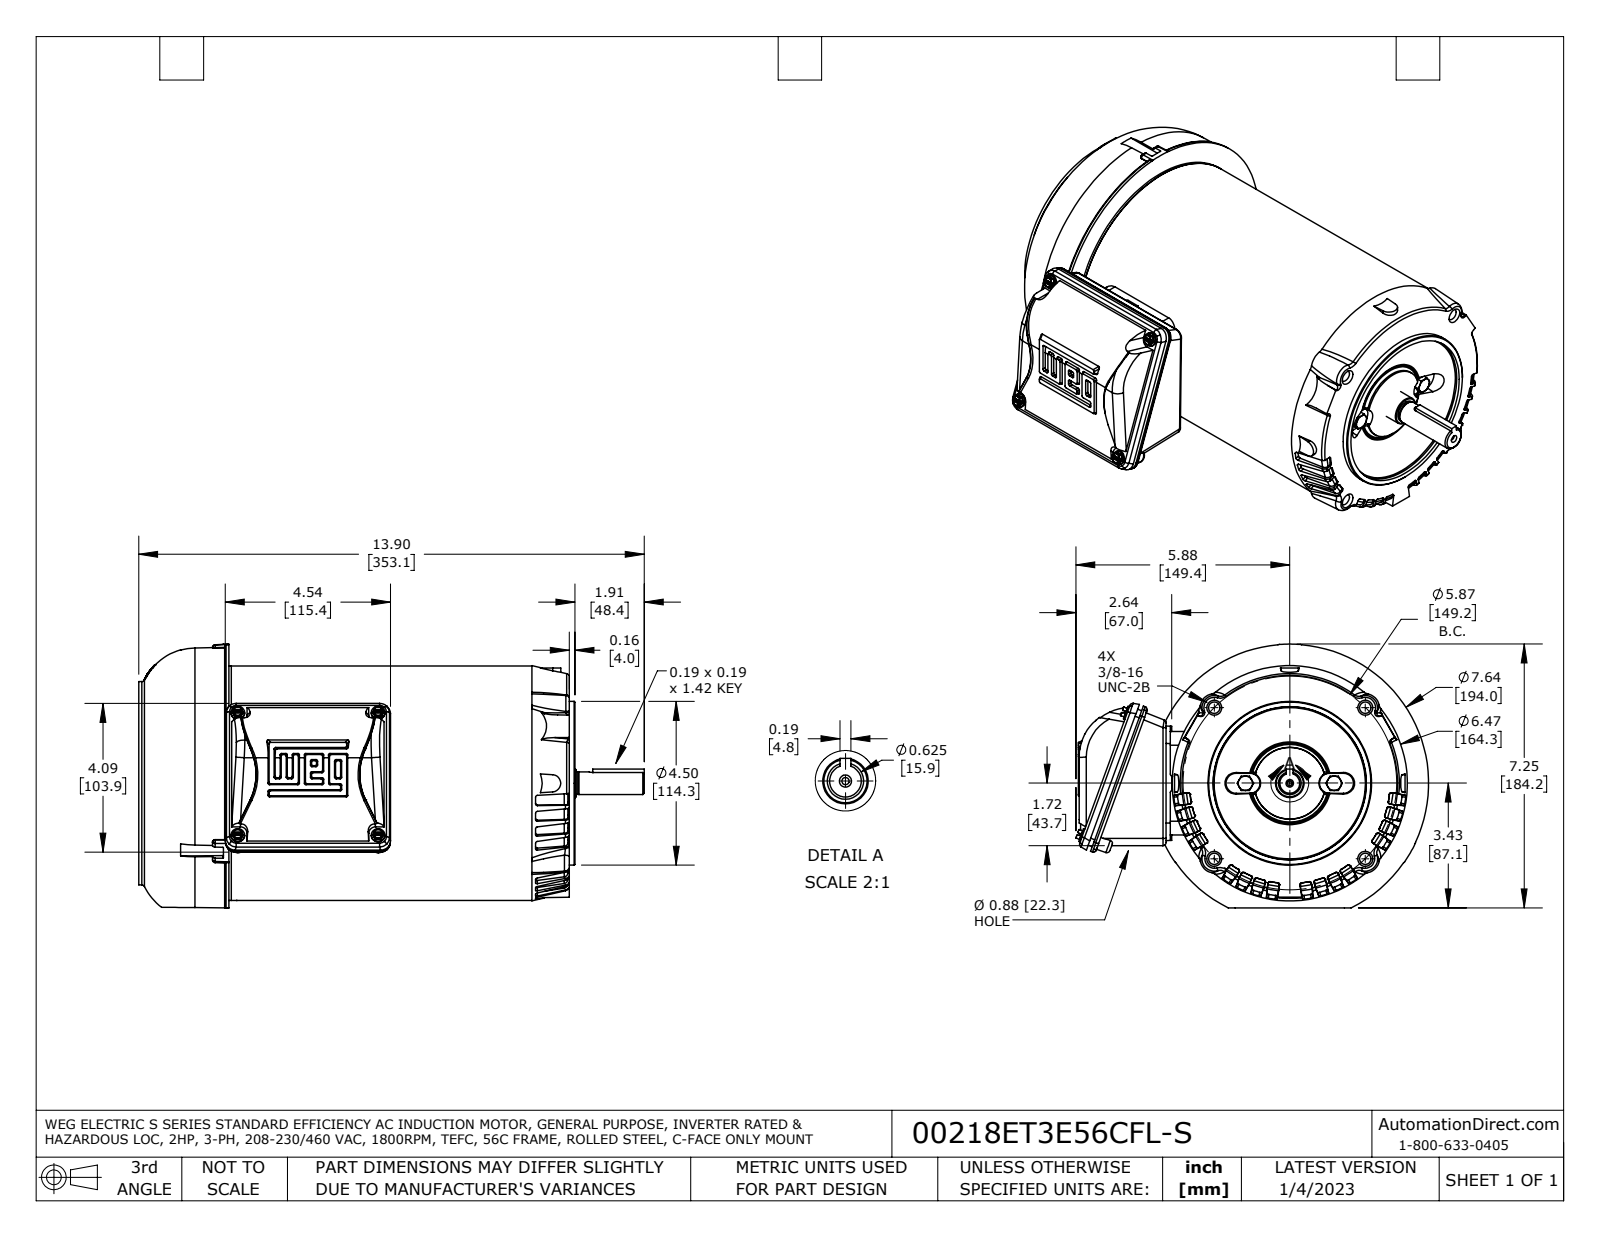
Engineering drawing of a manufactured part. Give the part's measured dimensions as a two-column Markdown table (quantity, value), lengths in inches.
| quantity | value |
| --- | --- |
| part name | 56C_3PH_TEFC_GP_13898_FL fxt |
| STEP written by | SolidWorks 2021 (AUTOMOTIVE_DESIGN) |
| units | inches |
| bodies | 13 solids, 1286 faces (476 planar, 275 cylindrical, 535 other) |
| overall size | 13.902 × 9.7 × 7.551 |
| volume | 433.1 in³ |
| surface area | 637.3 in² |
| round holes (diameter × count) | 0.313 × 4, 0.124 × 1 |
| round bosses / shafts (diameter × count) | 0.374 × 4, 0.35 × 2, 6.447 × 1, 6.447 × 1, 5.591 × 1, 4.5 × 1, 0.783 × 1, 0.625 × 1 |
| partial cylindrical surfaces (radius × count) | 0.047 × 40, 0.006 × 38, 0.051 × 32, 0.059 × 12, 0.087 × 12, 0.02 × 10, 0.205 × 8, 0.276 × 8 |
| main face-to-face distances | 8.268, 0.067, 8.335, 2.283, 2.35, 10.618, 11.642, 9.358, 9.291, 1.024 |
| hole center spacings | 2.937, 4.154, 5.874 |
